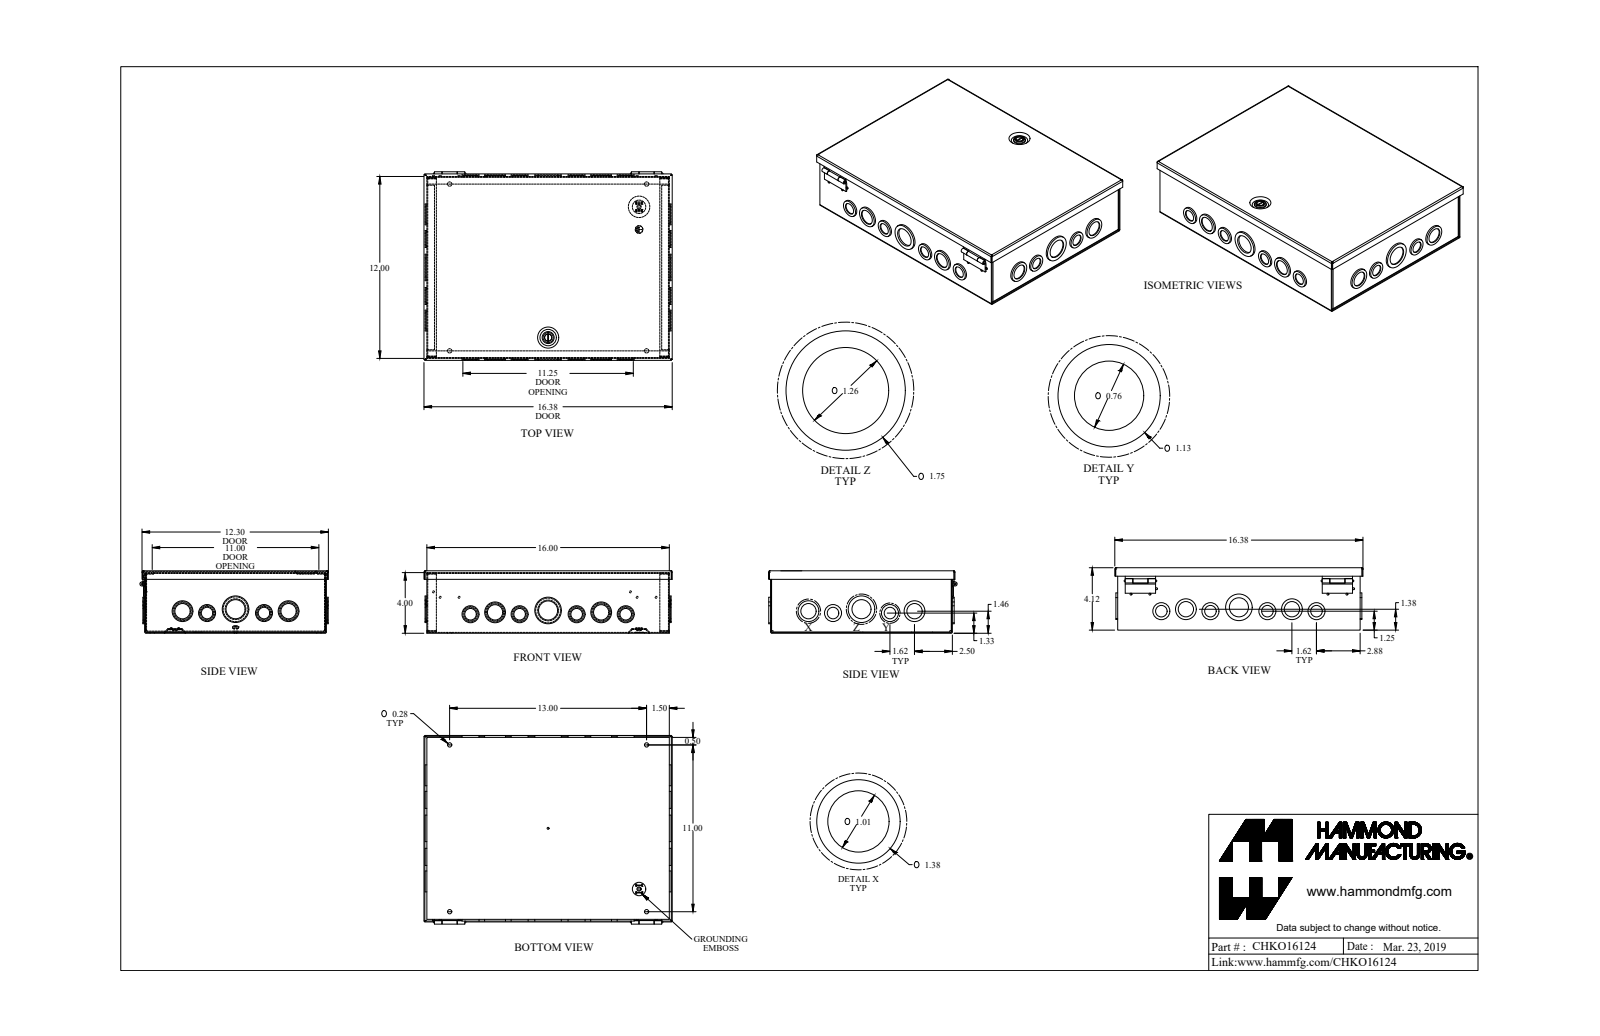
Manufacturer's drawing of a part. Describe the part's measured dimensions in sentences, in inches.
The part is named "CHKO16124_Default". Its 3-D file was written by "SolidWorks 2019 (CONFIG_CONTROL_DESIGN)". It is 12 solids with 775 faces: 368 planar, 364 cylindrical and 43 other. Overall it measures 16.38 by 12.443 by 4.118 inches. Its volume is 40.78 cubic inches and its surface area 1 437 square inches. Round holes: 10 of diameter 1.011, 6 of diameter 0.761, 6 of diameter 1.261, 4 of diameter 0.281, 2 of diameter 1.636, 1 of diameter 0.125, 1 of diameter 0.17, 1 of diameter 0.319, 1 of diameter 0.476, 1 of diameter 0.5. Round bosses or shafts: 8 of diameter 1.125, 8 of diameter 0.131, 6 of diameter 0.875, 4 of diameter 0.875, 3 of diameter 1.375, 3 of diameter 1.375, 2 of diameter 1.75, 2 of diameter 1.125. Partial cylindrical surfaces (rounded edges, fillets, slot ends): 16 of radius 0.029, 16 of radius 0.086, 8 of radius 0.057, 4 of radius 0.012, 4 of radius 0.1, 2 of radius 0.036, 2 of radius 0.079, 2 of radius 0.25. The main face-to-face distances are 0.057, 4.061, 4.118, 4.004, 11.943, 15.943, 12, 11.886, 16, 3.943. The hole center spacings are 1.625, 1.896, 3.502, 5.381, 7, 3.24, 3.76, 5.126.
